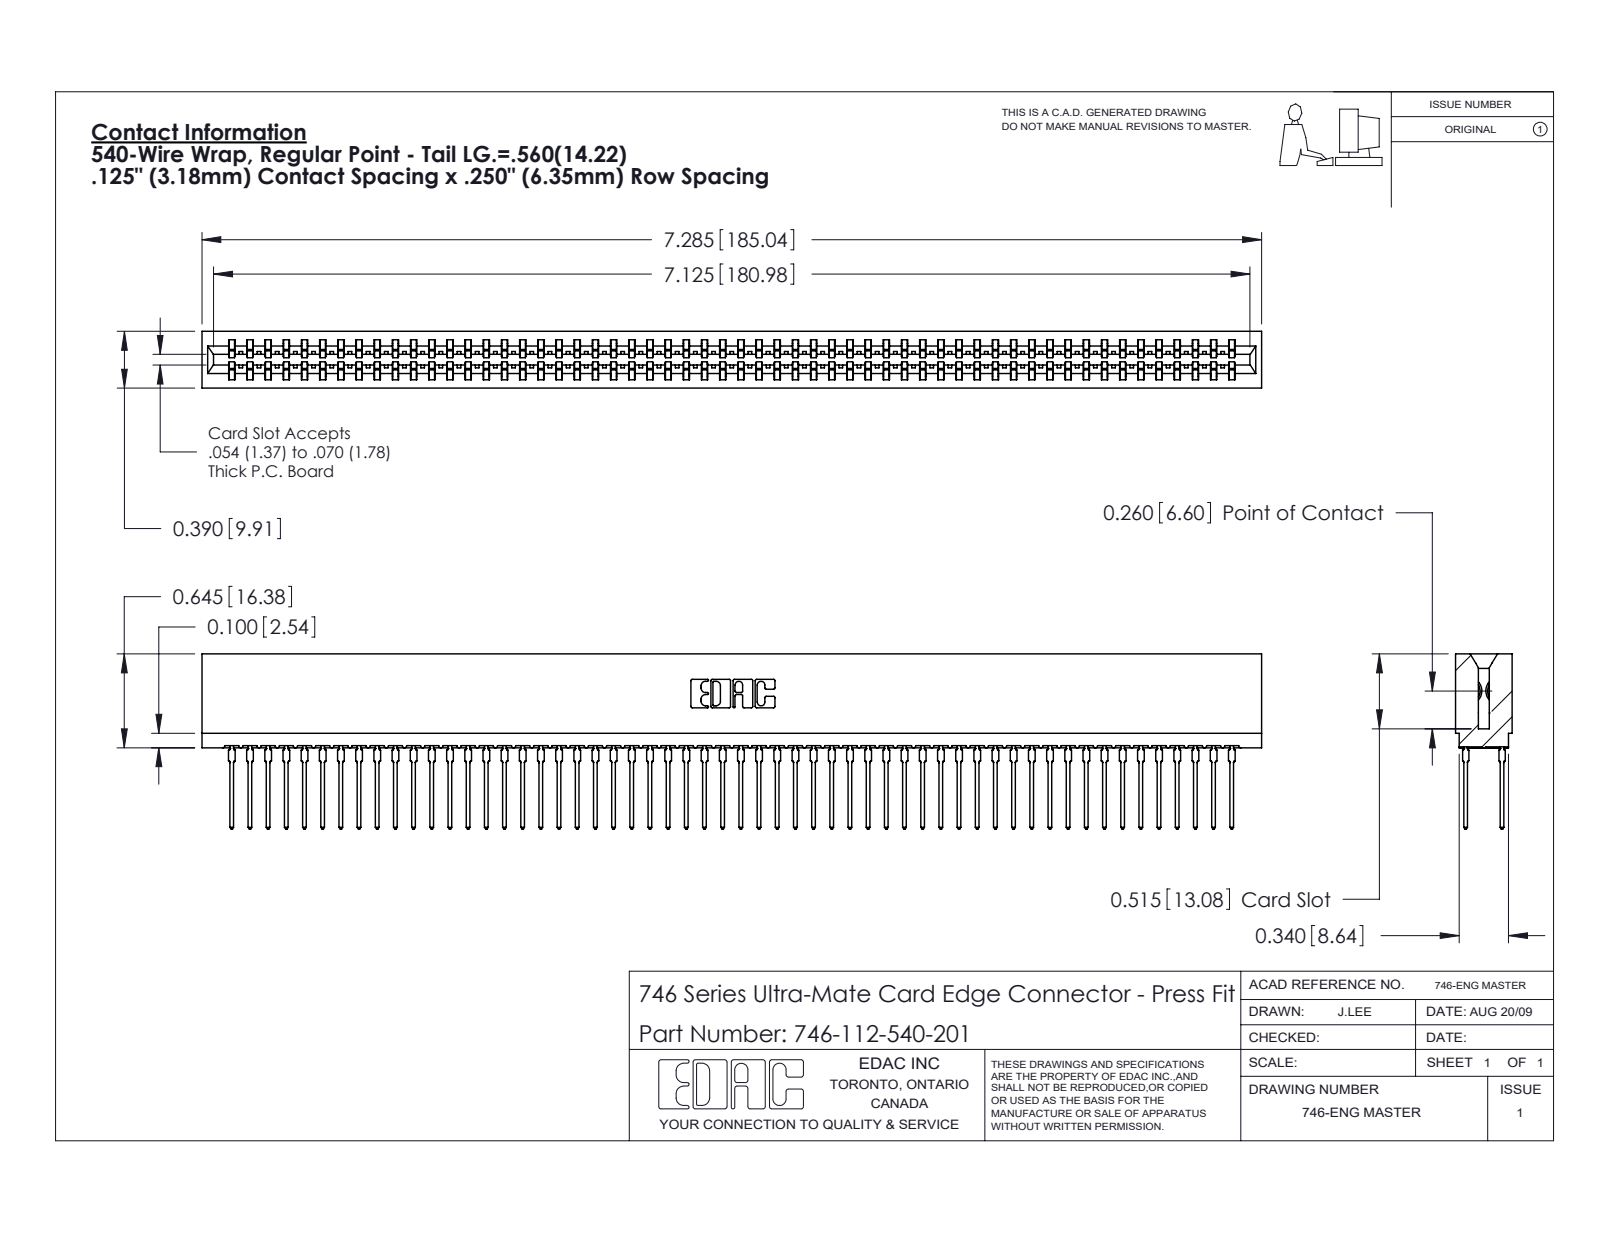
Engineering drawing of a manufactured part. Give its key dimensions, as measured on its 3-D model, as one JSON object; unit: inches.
{"part_name": "746 Part_.515 Slot Depth - 01; 746-292-001_540; 746-112-540-201", "step_written_by": "SolidWorks 2020 (CONFIG_CONTROL_DESIGN)", "units": "inches", "bodies": {"solids": 113, "faces": 10121, "planar": 5207, "cylindrical": 2002, "other": 2912}, "overall_size": [7.285, 1.204, 0.39], "volume_in3": 1.226, "surface_area_in2": 52.85, "partial_cylinders_radius": [[0.021, 224], [0.015, 57], [0.01, 22], [0.005, 8], [0.011, 8], [0.007, 6], [0.031, 6], [0.026, 3]], "face_to_face_distances": [0.057, 0.333, 0.25, 0.39, 0.025, 0.307, 0.083, 0.275, 0.174, 0.158]}
